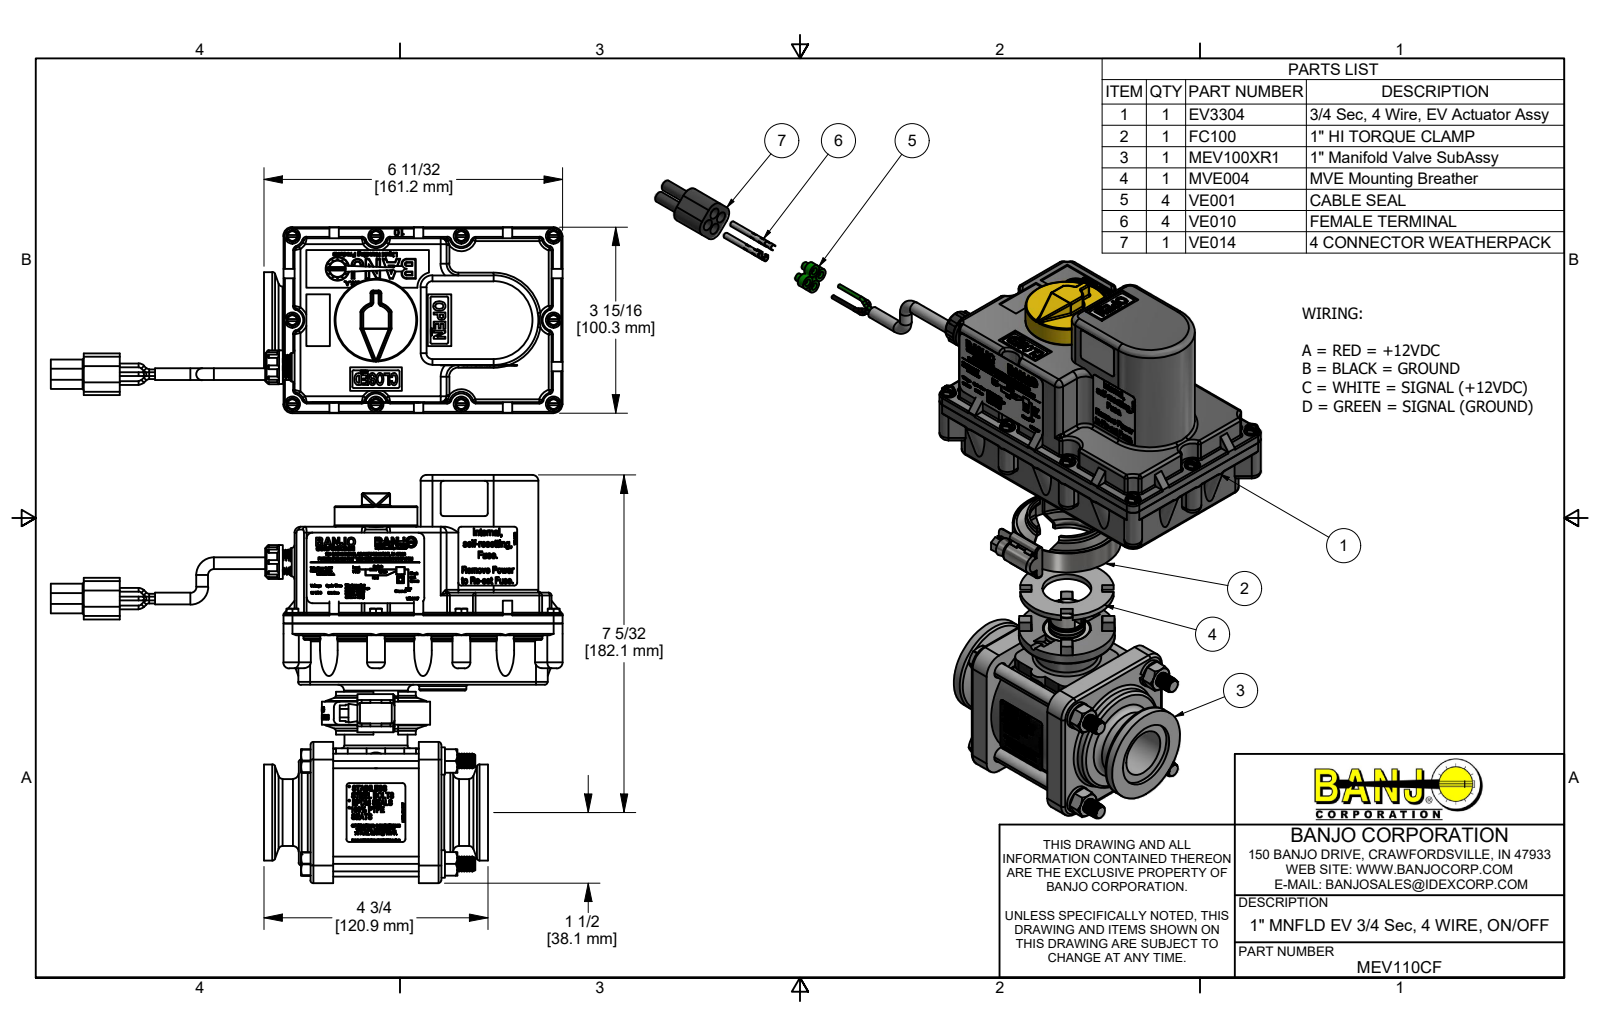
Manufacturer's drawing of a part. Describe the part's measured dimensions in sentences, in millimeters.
The part is named "MEV110CF; MEV100XR1; MEV10254A; MEV10254AX (+8 more)". Its 3-D file was written by "Autodesk Inventor 2019 (AUTOMOTIVE_DESIGN)". It is 81 solids with 14080 faces: 7056 planar, 1783 cylindrical and 5241 other. Overall it measures 276.1 by 220.2 by 100.3 millimeters. Its volume is 918 500 cubic millimeters and its surface area 406 500 square millimeters. Round holes: 10 of diameter 2.8, 10 of diameter 4.1, 10 of diameter 5.1, 8 of diameter 1.3, 8 of diameter 2, 6 of diameter 1.2, 6 of diameter 3, 6 of diameter 3.8, 6 of diameter 4.5, 4 of diameter 0.4, 4 of diameter 1.2, 4 of diameter 2.4. Round bosses or shafts: 60 of diameter 6.8, 19 of diameter 2, 10 of diameter 8.3, 10 of diameter 3.5, 8 of diameter 2.6, 7 of diameter 6.4, 4 of diameter 14.8, 4 of diameter 8. Partial cylindrical surfaces (rounded edges, fillets, slot ends): 132 of radius 0.8, 67 of radius 1.5, 62 of radius 0.5, 43 of radius 0.9, 32 of radius 3.2, 25 of radius 1.6, 24 of radius 8, 24 of radius 12.7. The main face-to-face distances are 3.2, 3.2, 58.4, 20.1, 27.9, 5.1, 65.2, 19.8, 33, 82. The hole center spacings are 42.7, 52.3, 42.8, 45.3, 60.4, 2.8, 7.1, 12.5.
